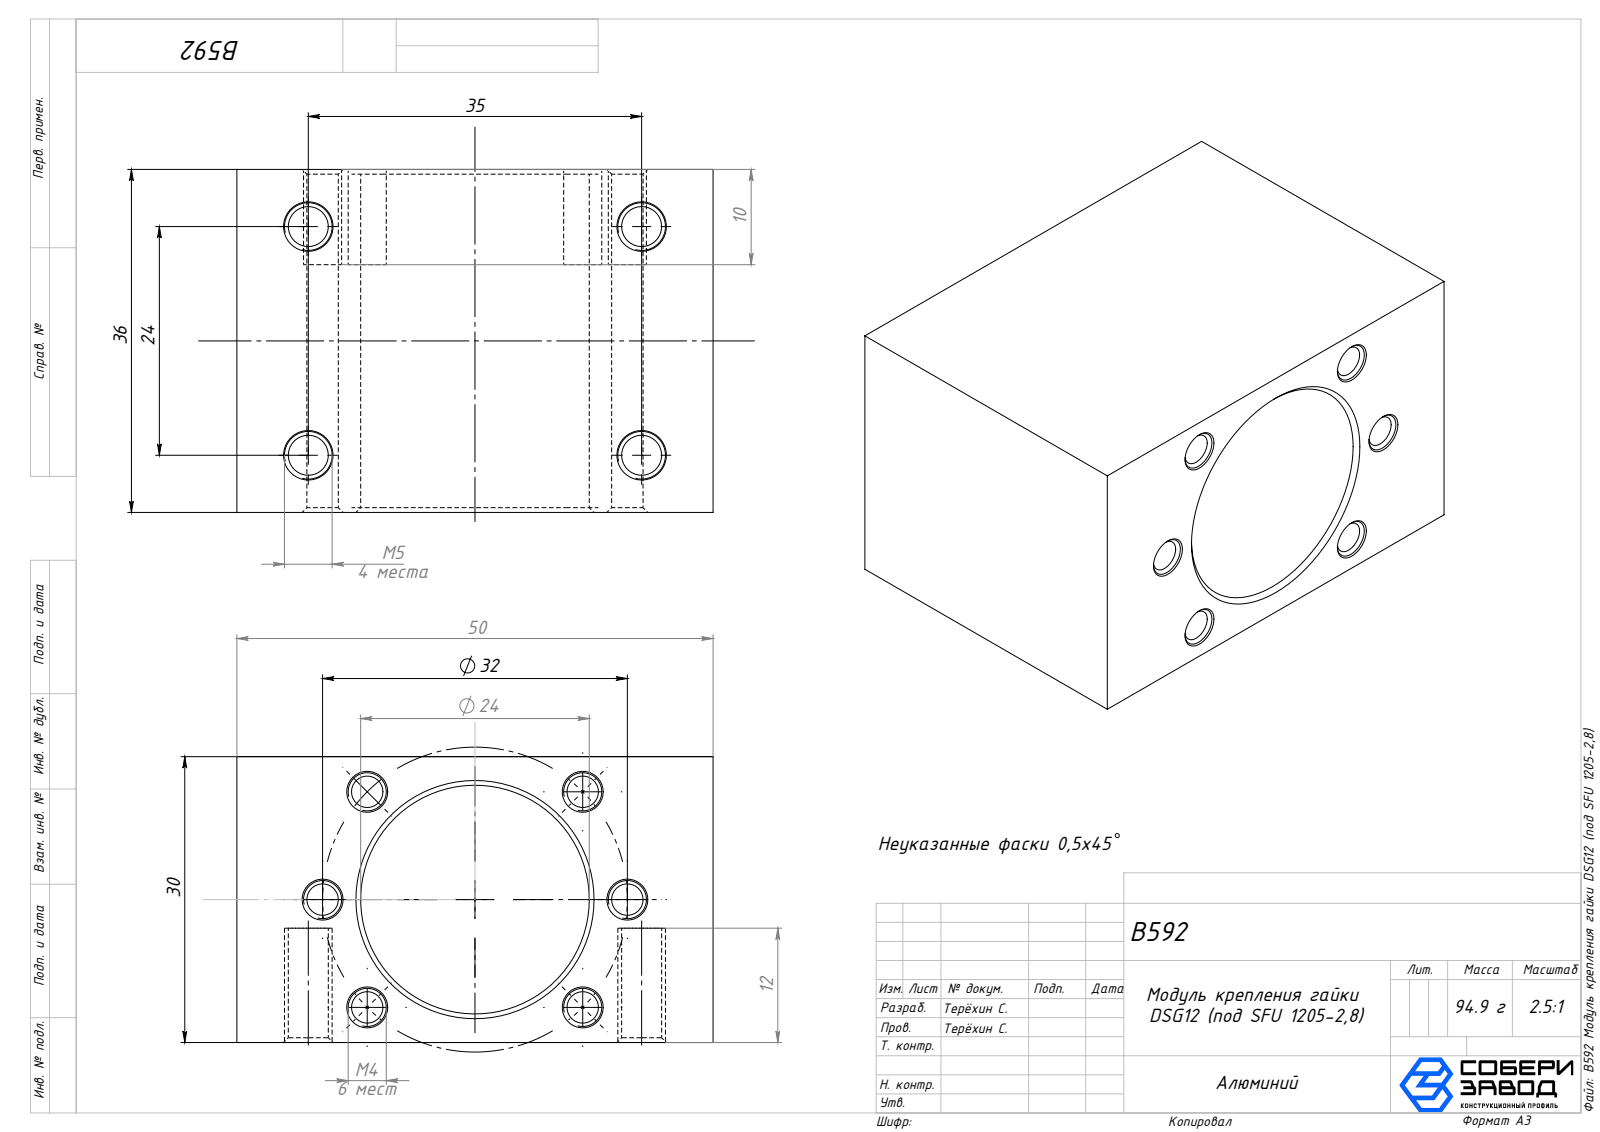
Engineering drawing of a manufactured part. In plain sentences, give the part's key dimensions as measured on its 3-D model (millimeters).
The part is named "B592 Модуль крепления гайки DSG12 (под SFU 1205-2,8)_00; Сборка1". Its 3-D file was written by "SolidWorks 2025 (AUTOMOTIVE_DESIGN)". It is 1 solid with 68 faces: 10 planar, 22 cylindrical and 36 other. Overall it measures 50 by 36 by 30 millimeters. Its volume is 35 158 cubic millimeters and its surface area 13 249 square millimeters. Round holes: 6 of diameter 3.3, 4 of diameter 4.2, 1 of diameter 24. The main face-to-face distances are 30, 50, 36, 12, 18. The hole center spacings are 16, 22.63, 32, 12.24, 12.25, 24, 29.56, 29.57.
